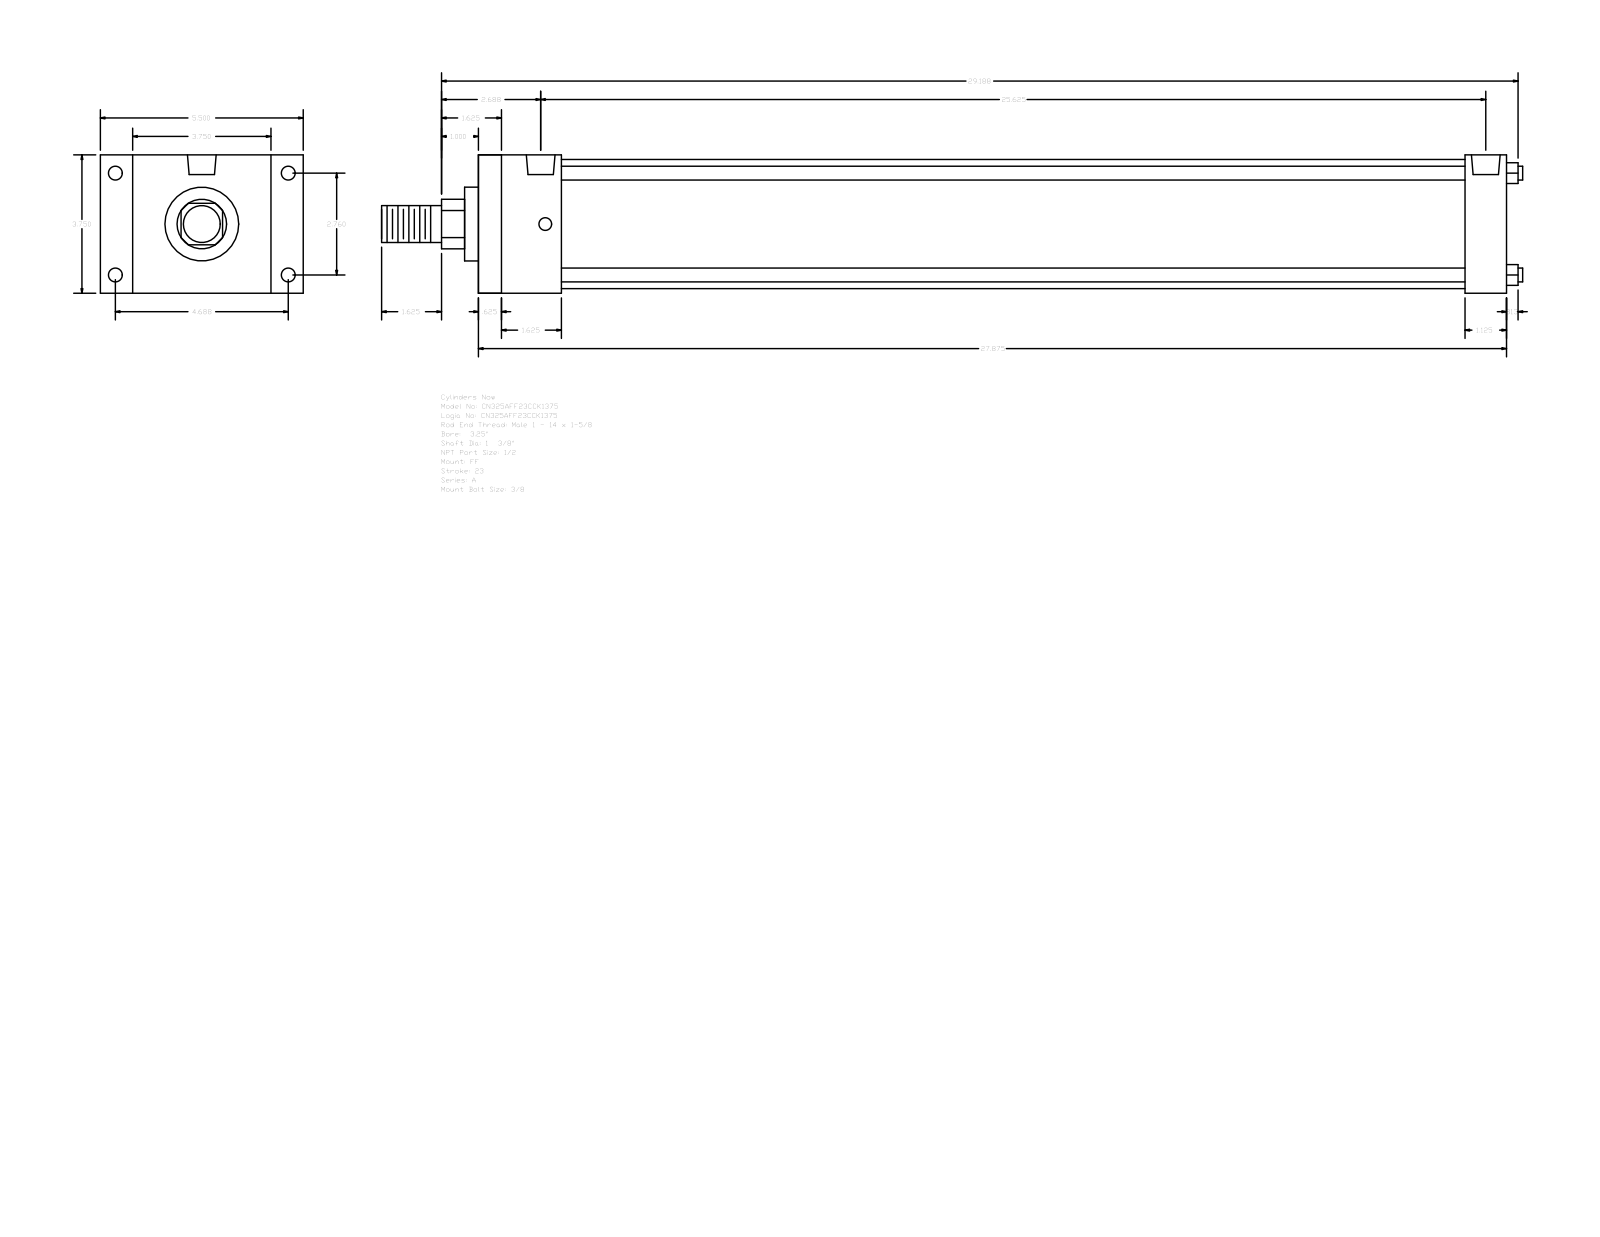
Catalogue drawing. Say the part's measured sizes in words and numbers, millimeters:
The part is named "A_FF__0325_1.375". Its 3-D file was written by "GSSL Pune (CONFIG_CONTROL_DESIGN)". It is 0 solids with 92 faces: 64 planar, 28 cylindrical and 0 other. Overall it measures 785.81 by 139.7 by 95.25 millimeters. Round holes: 4 of diameter 8.73, 4 of diameter 9.53, 2 of diameter 19.77. Round bosses or shafts: 4 of diameter 9.53, 1 of diameter 88.9, 1 of diameter 50.8, 1 of diameter 34.92, 1 of diameter 25.4. Partial cylindrical surfaces (rounded edges, fillets, slot ends): 1 of radius 17.06. The main face-to-face distances are 95.24, 708.02, 692.15, 15.87, 57.15, 22.23, 117.47, 28.57, 679.45, 41.28. The hole center spacings are 3.18, 70.1, 119.06, 138.16, 644.52, 647.7, 650.88.
